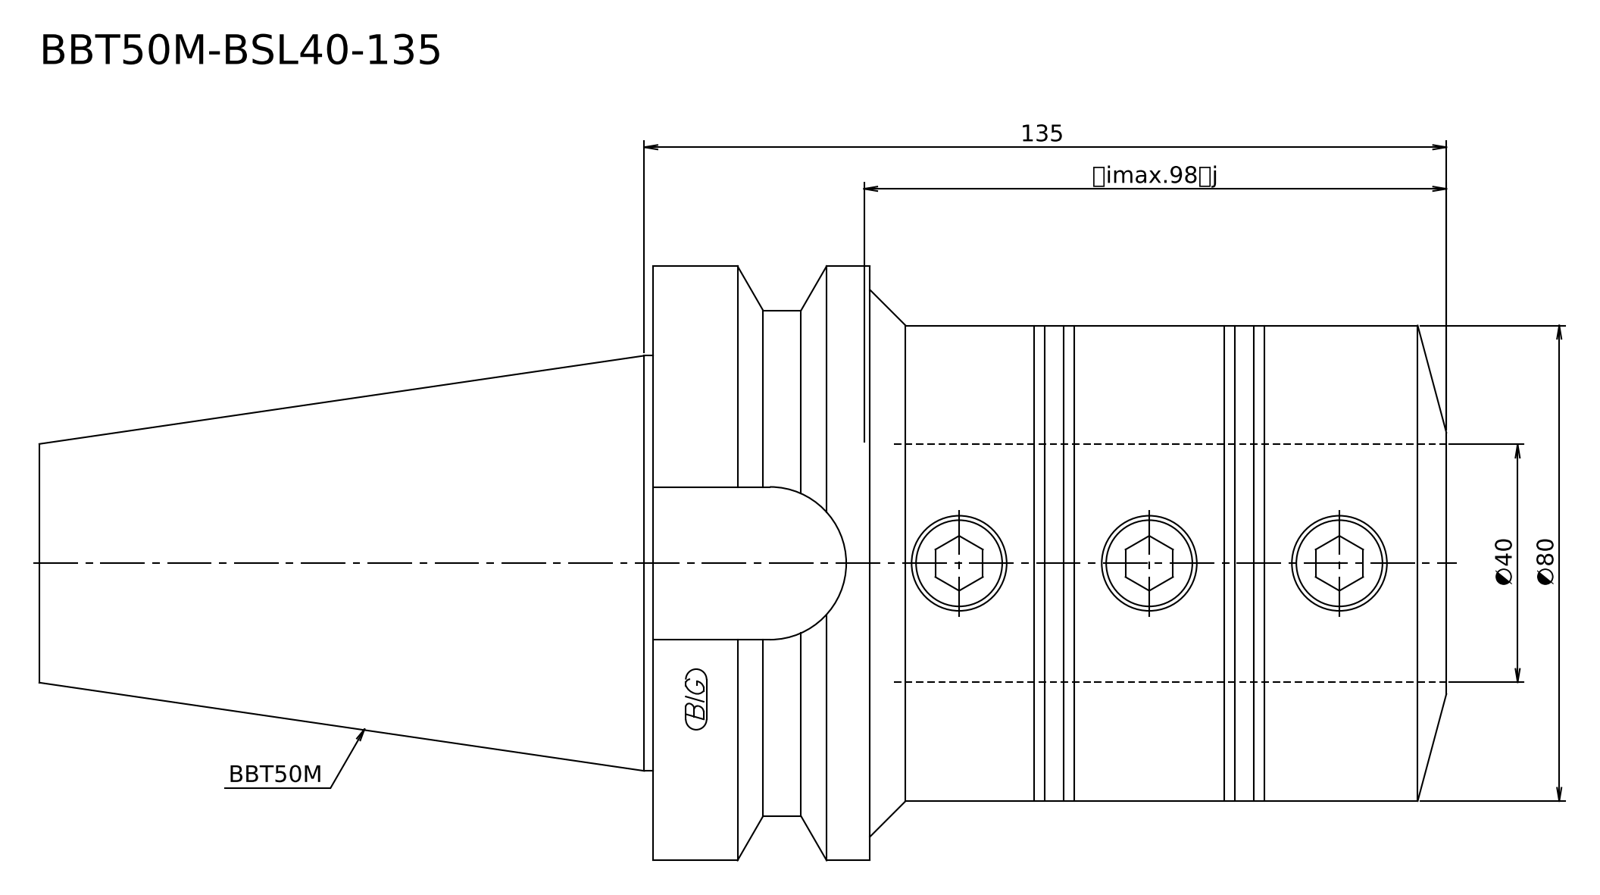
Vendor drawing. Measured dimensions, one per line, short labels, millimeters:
written by: Kubotek KeyCreator V8.5.1 (14335) (CONFIG_CONTROL_DESIGN)
unit: mm
bodies: 1 solid, 14 faces (4 planar, 5 cylindrical, 5 other)
size: 236.8 × 100 × 100
volume: 999 731 mm³; area: 67 183 mm²
bosses: 1× ⌀100, 1× ⌀85, 1× ⌀80, 1× ⌀69.85
face distances: 133.5, 236.8, 103.3, 97, 36.5, 139.8
